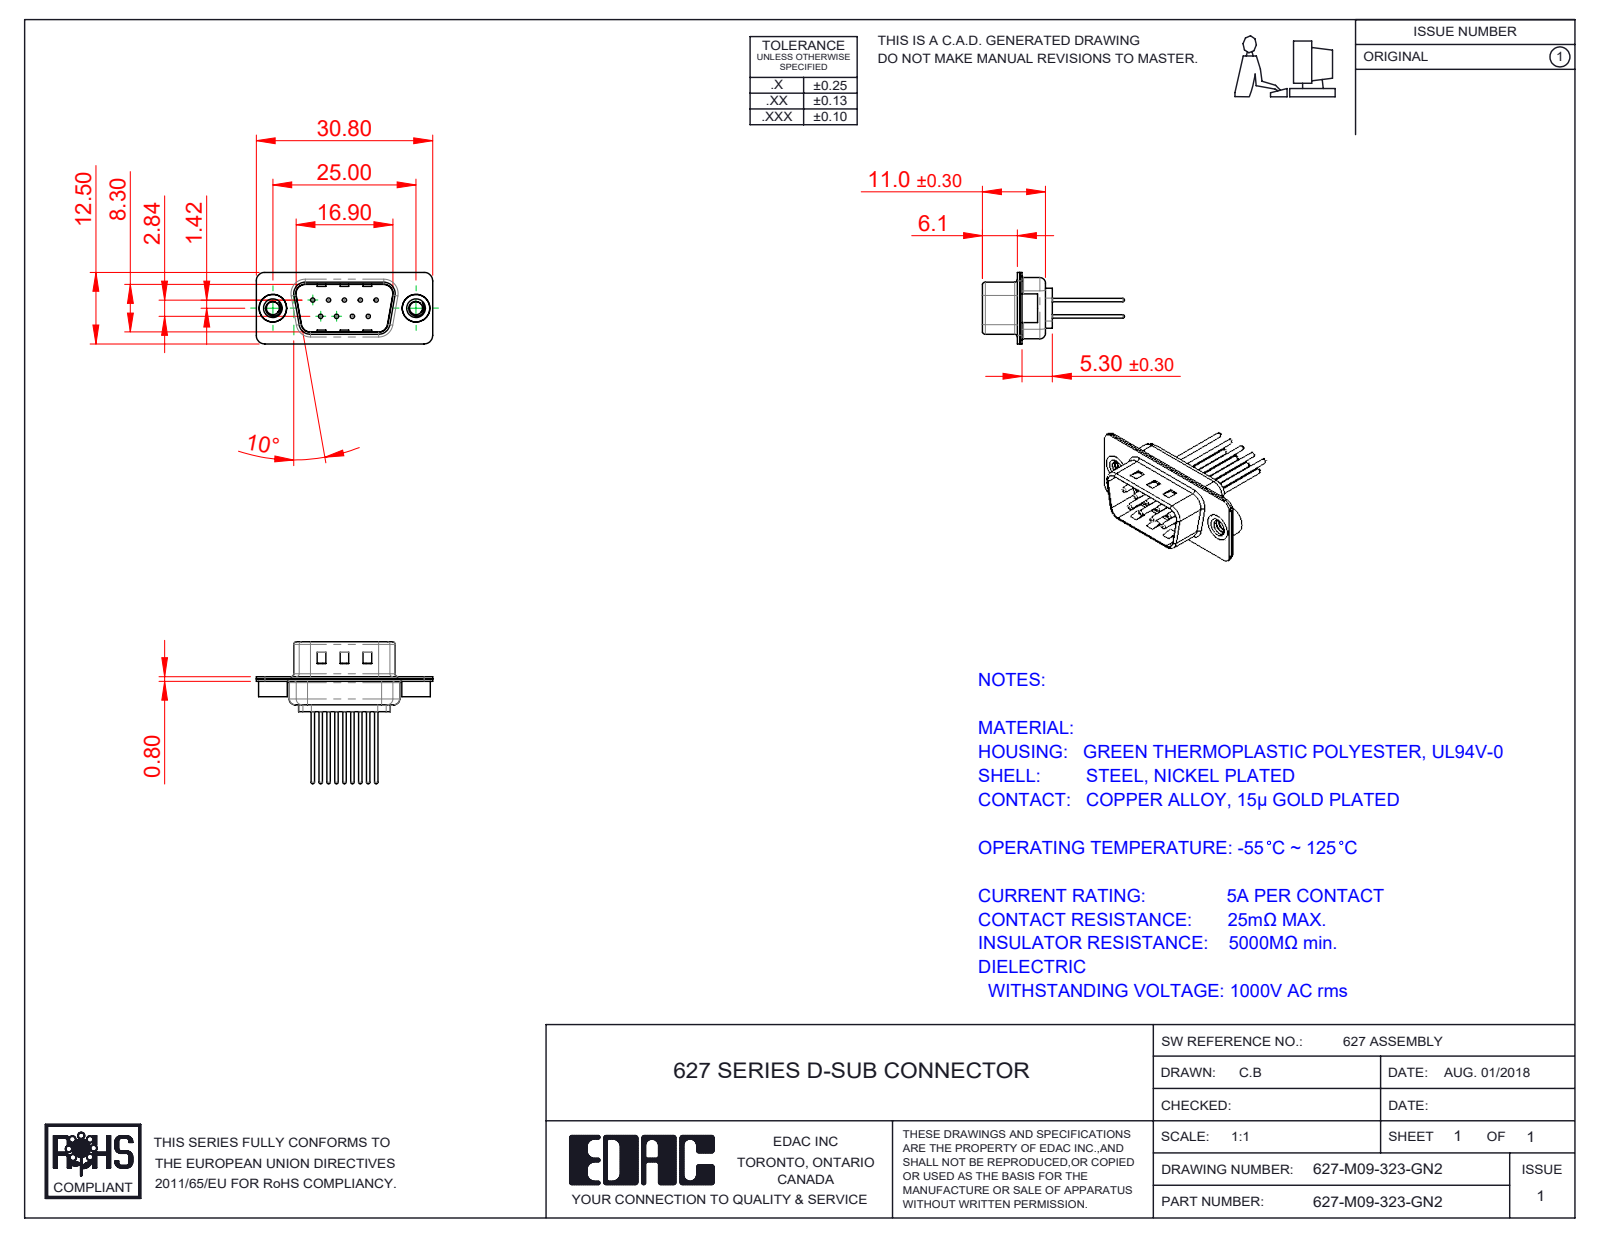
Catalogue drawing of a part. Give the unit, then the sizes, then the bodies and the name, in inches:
Units: inches
Overall size (bounding box): 1.213 × 0.975 × 0.492
Round holes (diameter × count): ⌀0.03 ×9, ⌀0.063 ×9, ⌀0.079 ×9, ⌀0.089 ×2, ⌀0.157 ×2, ⌀0.189 ×2
Round bosses / shafts (diameter × count): ⌀0.059 ×9, ⌀0.024 ×9, ⌀0.197 ×2, ⌀0.193 ×2
Partial cylindrical surfaces — rounded edges, fillets, slot ends (radius × count): R0.059 ×16, R0.079 ×12, R0.02 ×8, R0.063 ×8, R0.01 ×4, R0.024 ×4, R0.026 ×4, R0.035 ×4
Main face-to-face distances: 0.016, 0.031, 0.374, 0.358, 0.343, 0.026, 0.39, 0.047, 0.24, 0.209
Hole centre spacings: 0.124, 0.109, 0.218, 0.198, 0.198, 0.327, 0.28, 0.294
Volume: 0.081 in³ · Surface area: 5.721 in²
Bodies: 14 solids, 637 faces (170 planar, 255 cylindrical, 212 other)
Part name (STEP PRODUCT): 627M Shell Rear_09 Contacts; 627M Shell Front_09 Contacts; 627M Housing_09 Contacts; 627M 4-40 Threaded Rivet (+3 more)
STEP written by: SolidWorks 2020 (CONFIG_CONTROL_DESIGN)
